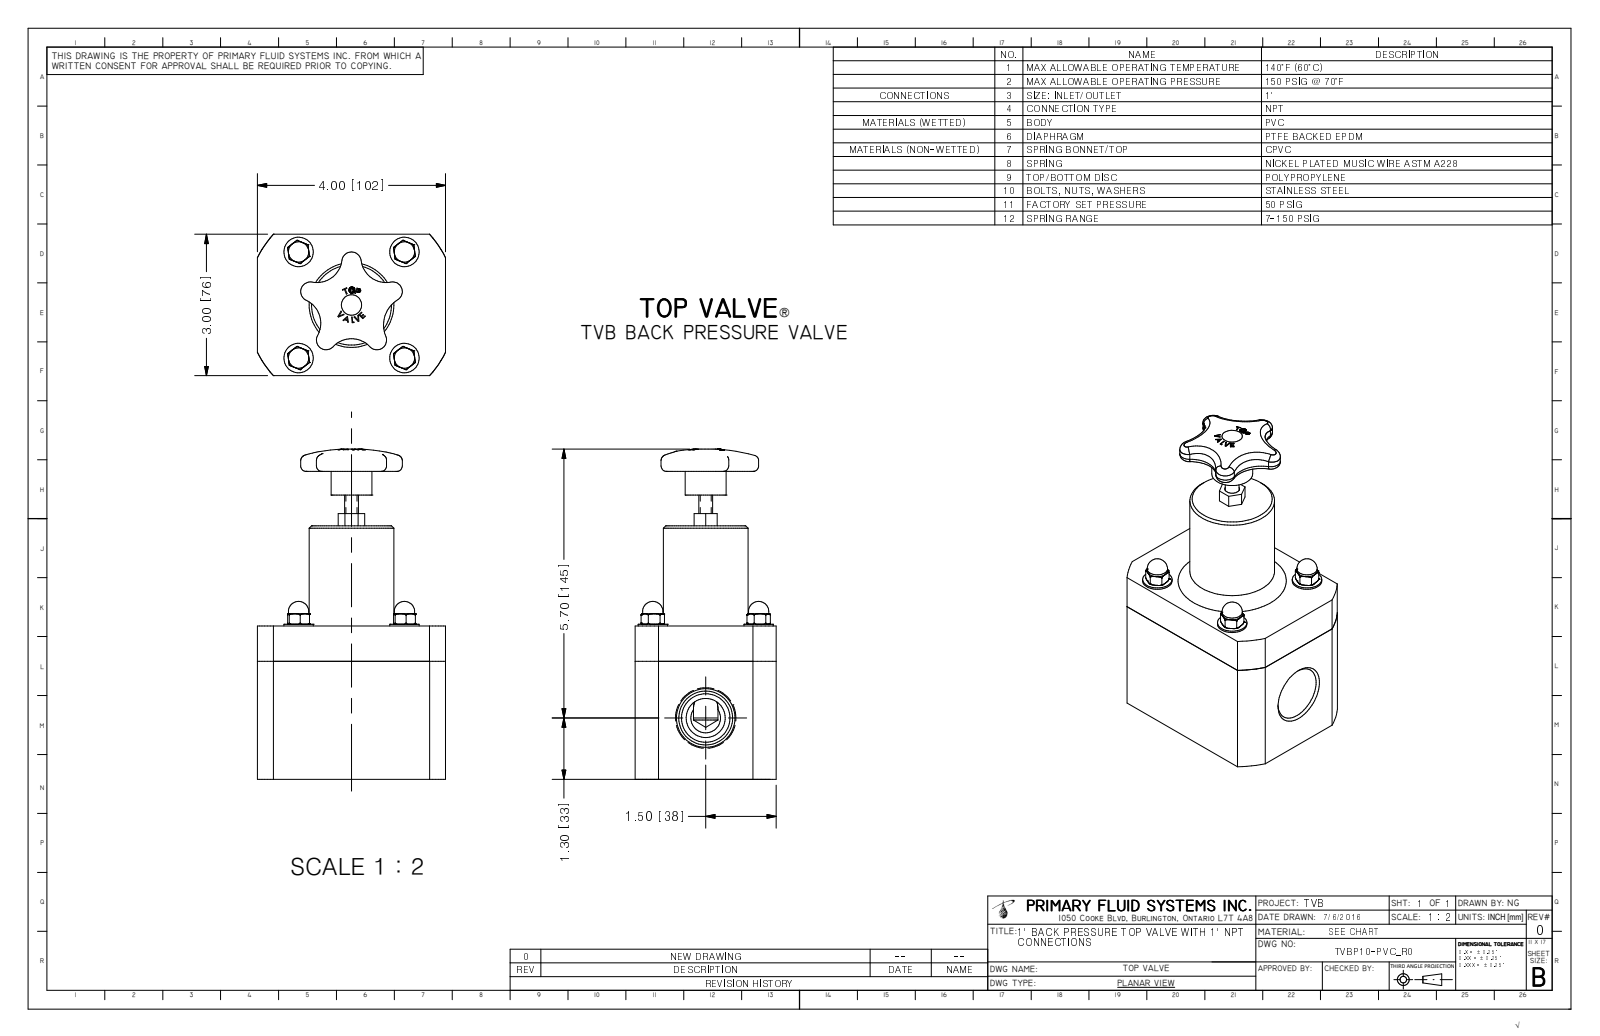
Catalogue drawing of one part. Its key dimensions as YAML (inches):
part_name: "TVBP10-PVC_R0"
step_written_by: "Autodesk Inventor 2009 (AUTOMOTIVE_DESIGN)"
units: inches
bodies: {solids: 1, faces: 345, planar: 148, cylindrical: 49, other: 148}
overall_size: [7.002, 4, 3]
volume: 42.89
surface_area: 100.4
round_holes:
  - {diameter: 0.175, count: 4}
  - {diameter: 1.144, count: 1}
round_bosses_or_shafts:
  - {diameter: 0.625, count: 4}
  - {diameter: 0.433, count: 4}
  - {diameter: 0.375, count: 4}
  - {diameter: 1.8, count: 1}
  - {diameter: 0.87, count: 1}
  - {diameter: 0.293, count: 1}
partial_cylinders:
  - {radius: 0.085, count: 5}
  - {radius: 0.205, count: 5}
  - {radius: 0.536, count: 4}
  - {radius: 0.656, count: 4}
  - {radius: 0.625, count: 1}
  - {radius: 0.745, count: 1}
  - {radius: 2.238, count: 1}
  - {radius: 2.238, count: 1}
face_to_face_distances: [3, 3.25, 4, 5.375, 2.125, 1, 2, 3.286, 0.036, 2.089]
hole_center_spacings: [2.25, 3.182]
